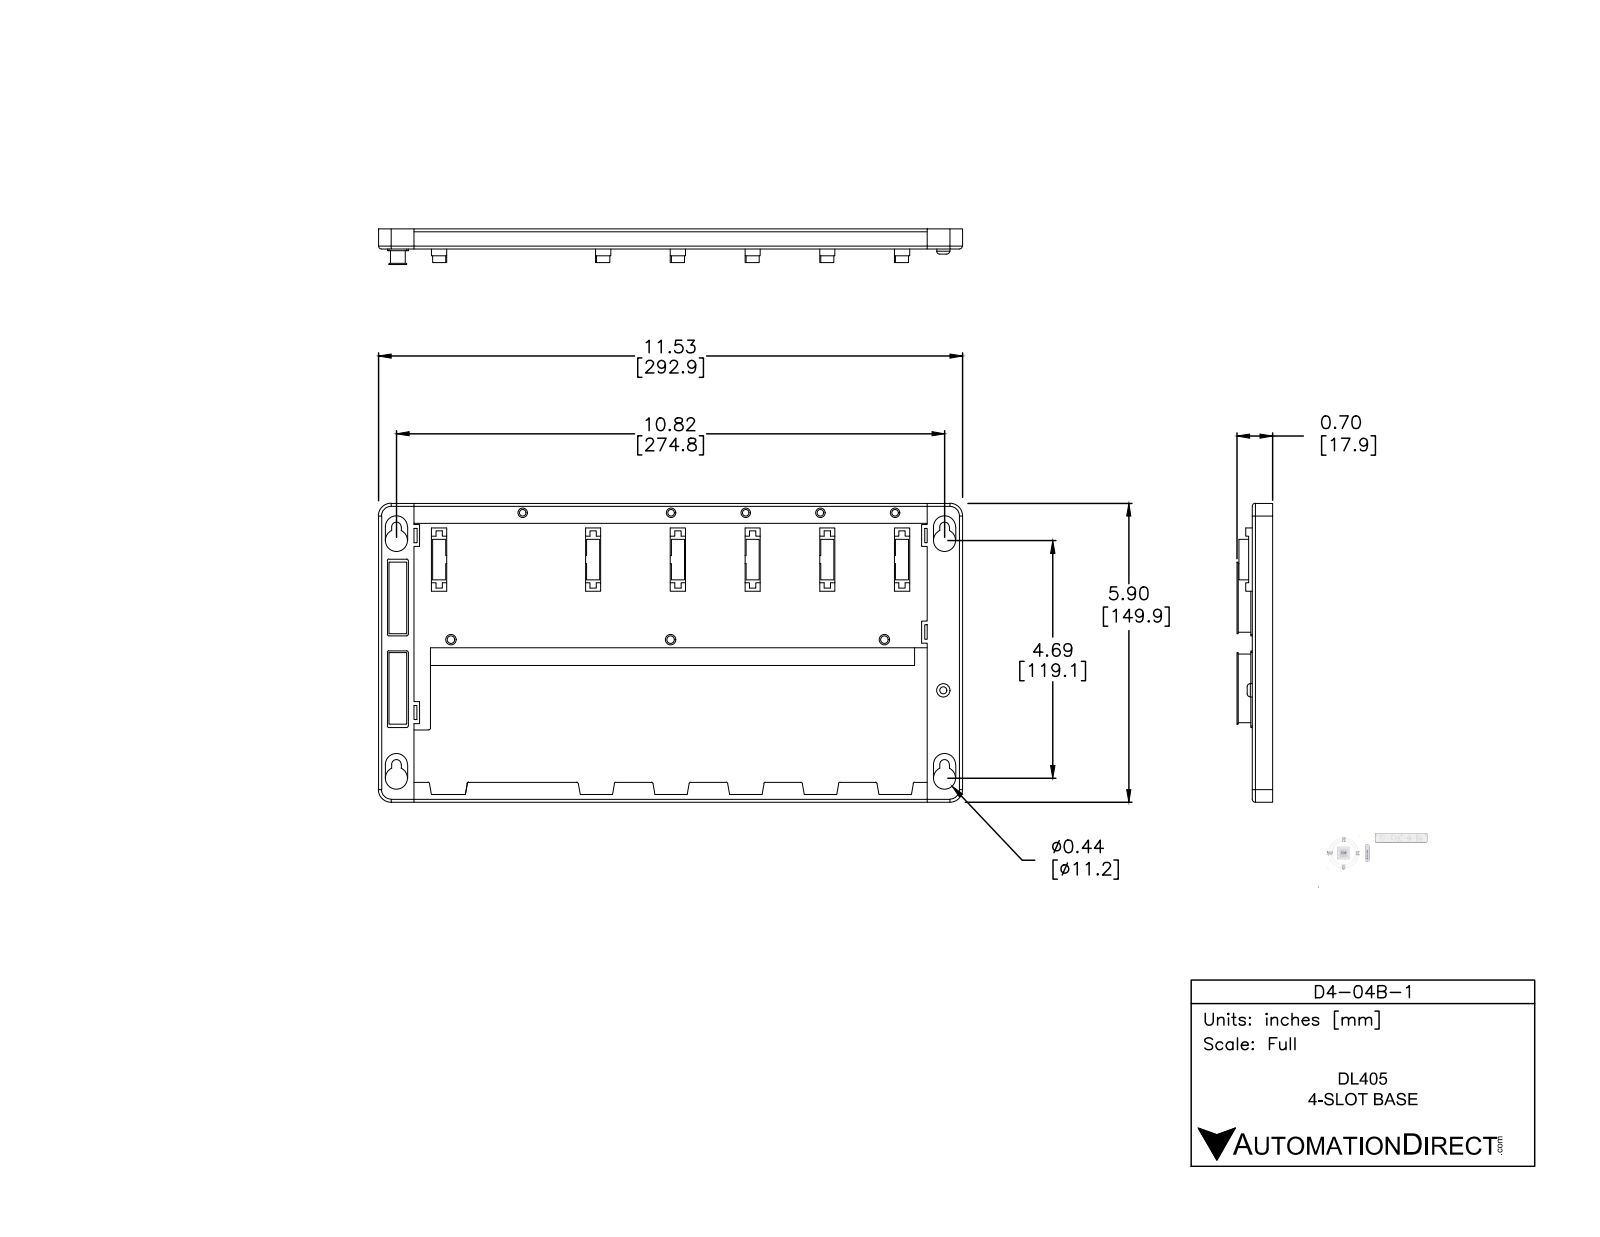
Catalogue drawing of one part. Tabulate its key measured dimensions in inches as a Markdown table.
| quantity | value |
| --- | --- |
| part name | D4-04B-1 |
| STEP written by | SolidWorks 2014 (AUTOMOTIVE_DESIGN) |
| units | inches |
| bodies | 1 solid, 450 faces (350 planar, 78 cylindrical, 22 other) |
| overall size | 11.53 × 5.9 × 0.706 |
| volume | 9.805 in³ |
| surface area | 246.2 in² |
| round holes (diameter × count) | 0.13 × 4, 0.44 × 4, 0.14 × 1 |
| round bosses / shafts (diameter × count) | 0.205 × 2, 0.26 × 1, 0.234 × 1, 0.222 × 1, 0.205 × 1 |
| partial cylindrical surfaces (radius × count) | 0.03 × 22, 0.06 × 6, 0.095 × 4, 0.19 × 4, 0.22 × 4, 0.25 × 4 |
| main face-to-face distances | 0.05, 0.197, 0.147, 0.275, 0.225, 0.078, 0.35, 0.125, 0.3, 0.4 |
| hole center spacings | 1.475, 2.95, 4.69, 10.82, 11.793, 1.119, 1.475, 2.511 |
